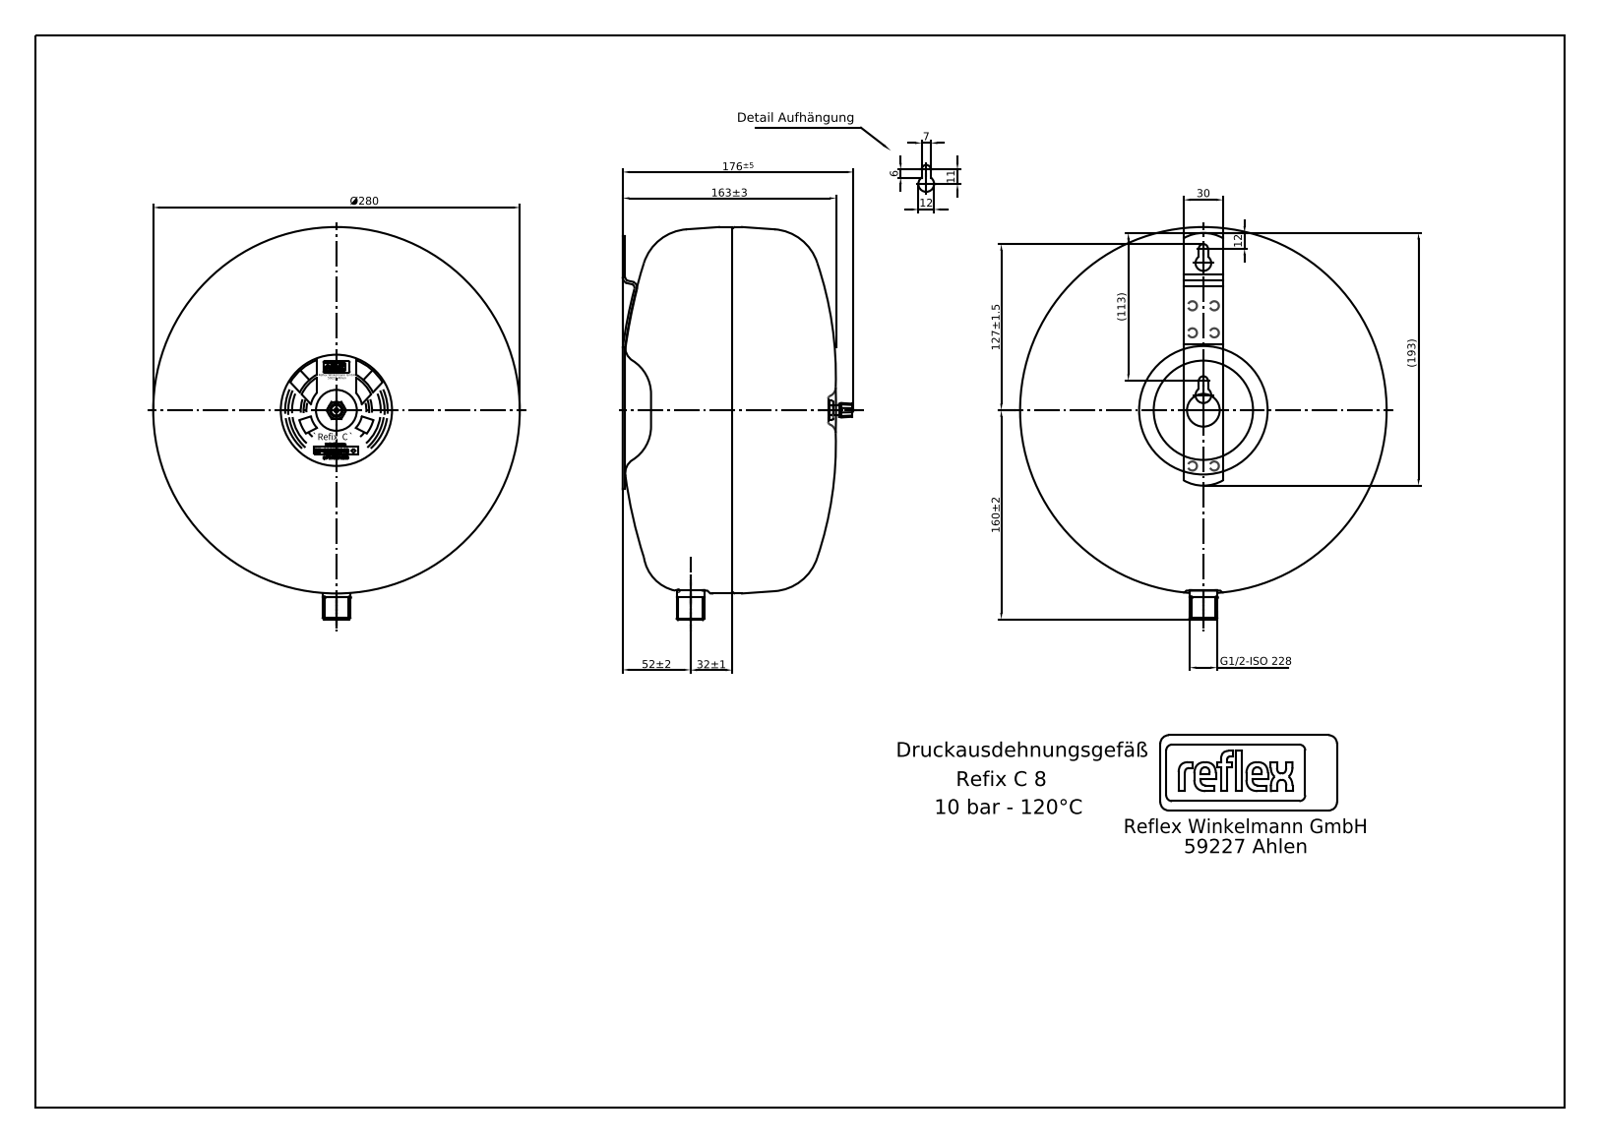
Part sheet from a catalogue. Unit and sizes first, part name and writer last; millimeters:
Units: millimetres
Overall size (bounding box): 300.5 × 280 × 163.5
Round holes (diameter × count): ⌀12 ×2
Round bosses / shafts (diameter × count): ⌀280 ×1, ⌀21.3 ×1, ⌀15 ×1, ⌀11 ×1, ⌀8 ×1
Partial cylindrical surfaces — rounded edges, fillets, slot ends (radius × count): R1.41 ×4, R0.56 ×3, R0.96 ×2, R1.69 ×2, R2.32 ×2, R2.35 ×2, R3 ×2, R3.18 ×2
Main face-to-face distances: 1.95, 2.08, 20, 21.95, 22.08, 121, 141, 142.95, 143.08, 30
Hole centre spacings: 101
Volume: 8 164 000 mm³ · Surface area: 229 438 mm²
Bodies: 9 solids, 143 faces (73 planar, 44 cylindrical, 26 other)
STEP written by: Mechanical Desktop 2011 (CONFIG_CONTROL_DESIGN)
